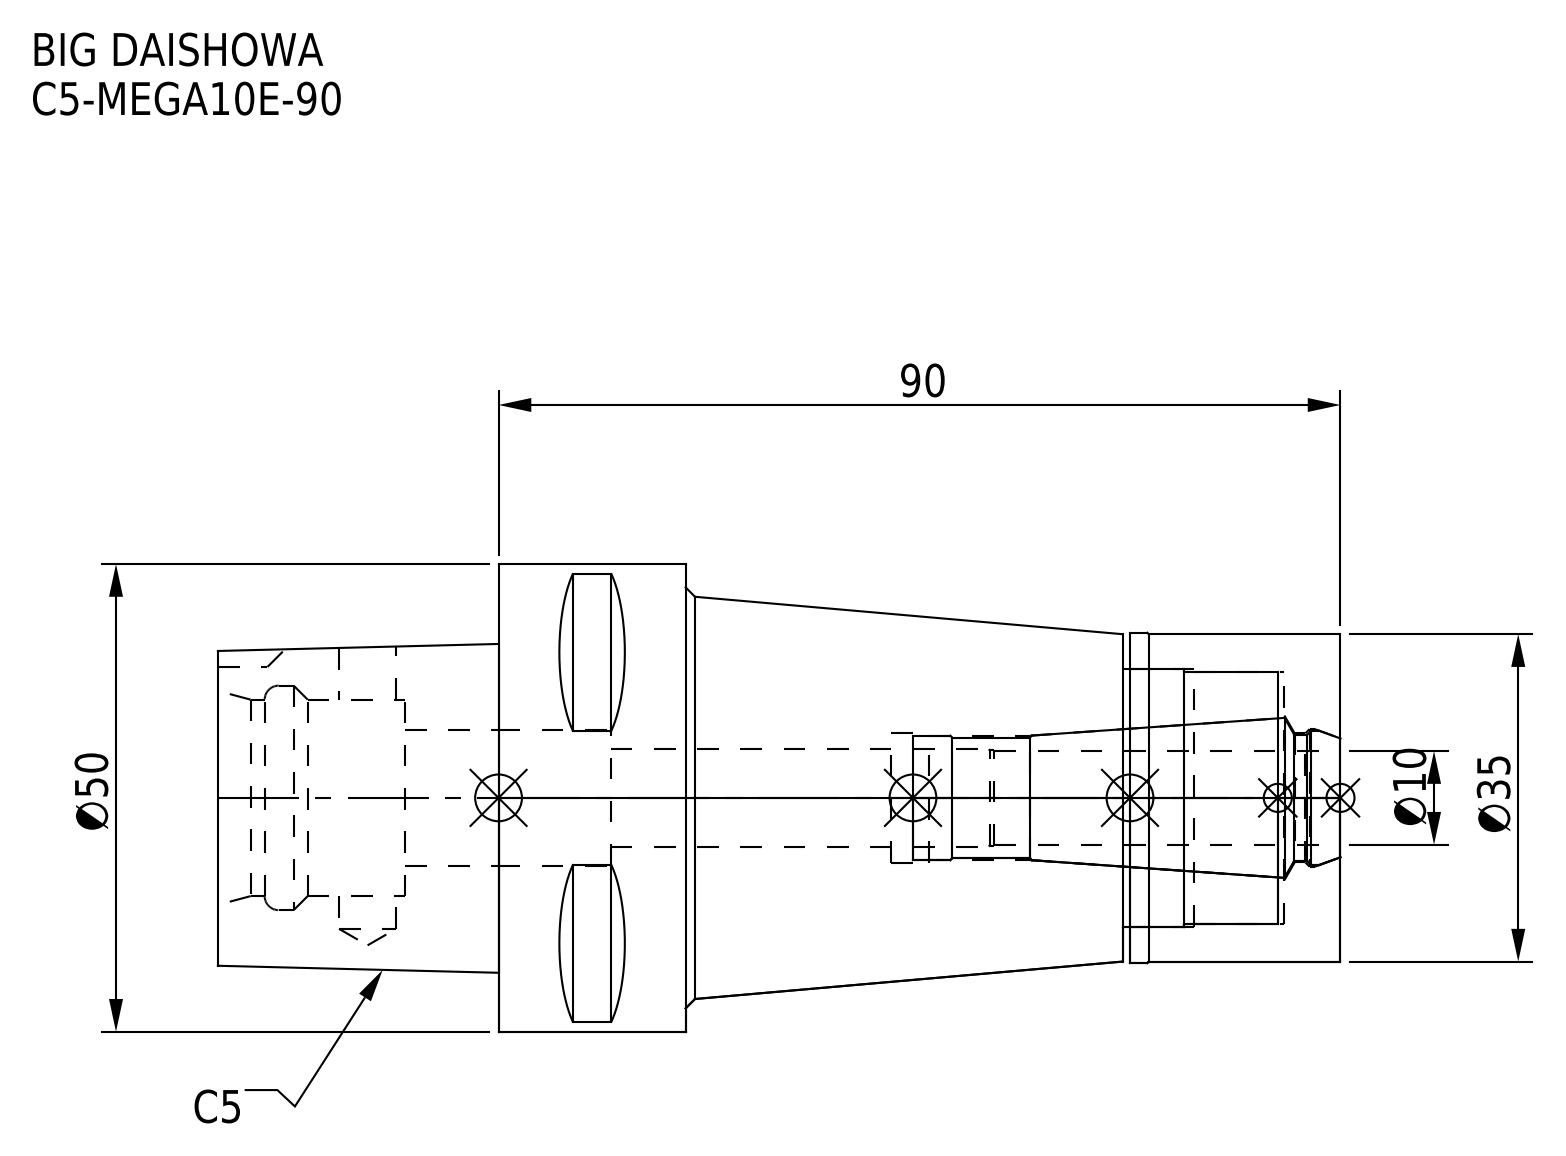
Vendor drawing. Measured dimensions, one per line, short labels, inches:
name: C5-MEGA10E-90; C5-MEGA10E-90-100-FreeParts; C5-MEGA10E-90-100_ASM.stp; C5-MEGA10E-90-100.stp (+3 more)
written by: SolidWorks 2019 (CONFIG_CONTROL_DESIGN)
unit: in
bodies: 2 solids, 97 faces (36 planar, 37 cylindrical, 24 other)
size: 4.724 × 1.969 × 1.969
volume: 7.452 in³; area: 43.43 in²
holes: 1× ⌀0.24, 1× ⌀0.409, 1× ⌀0.524, 1× ⌀0.543, 1× ⌀0.547, 1× ⌀0.571, 1× ⌀0.579, 1× ⌀0.827, 1× ⌀0.945, 1× ⌀1.063, 1× ⌀1.083
bosses: 1× ⌀1.969, 1× ⌀1.39, 1× ⌀1.378
rounds: 1× R0.157
face distances: 3.543, 1.181, 0.787, 0.886, 2.657, 4.724, 3.839, 2.626, 2.756, 1.87
